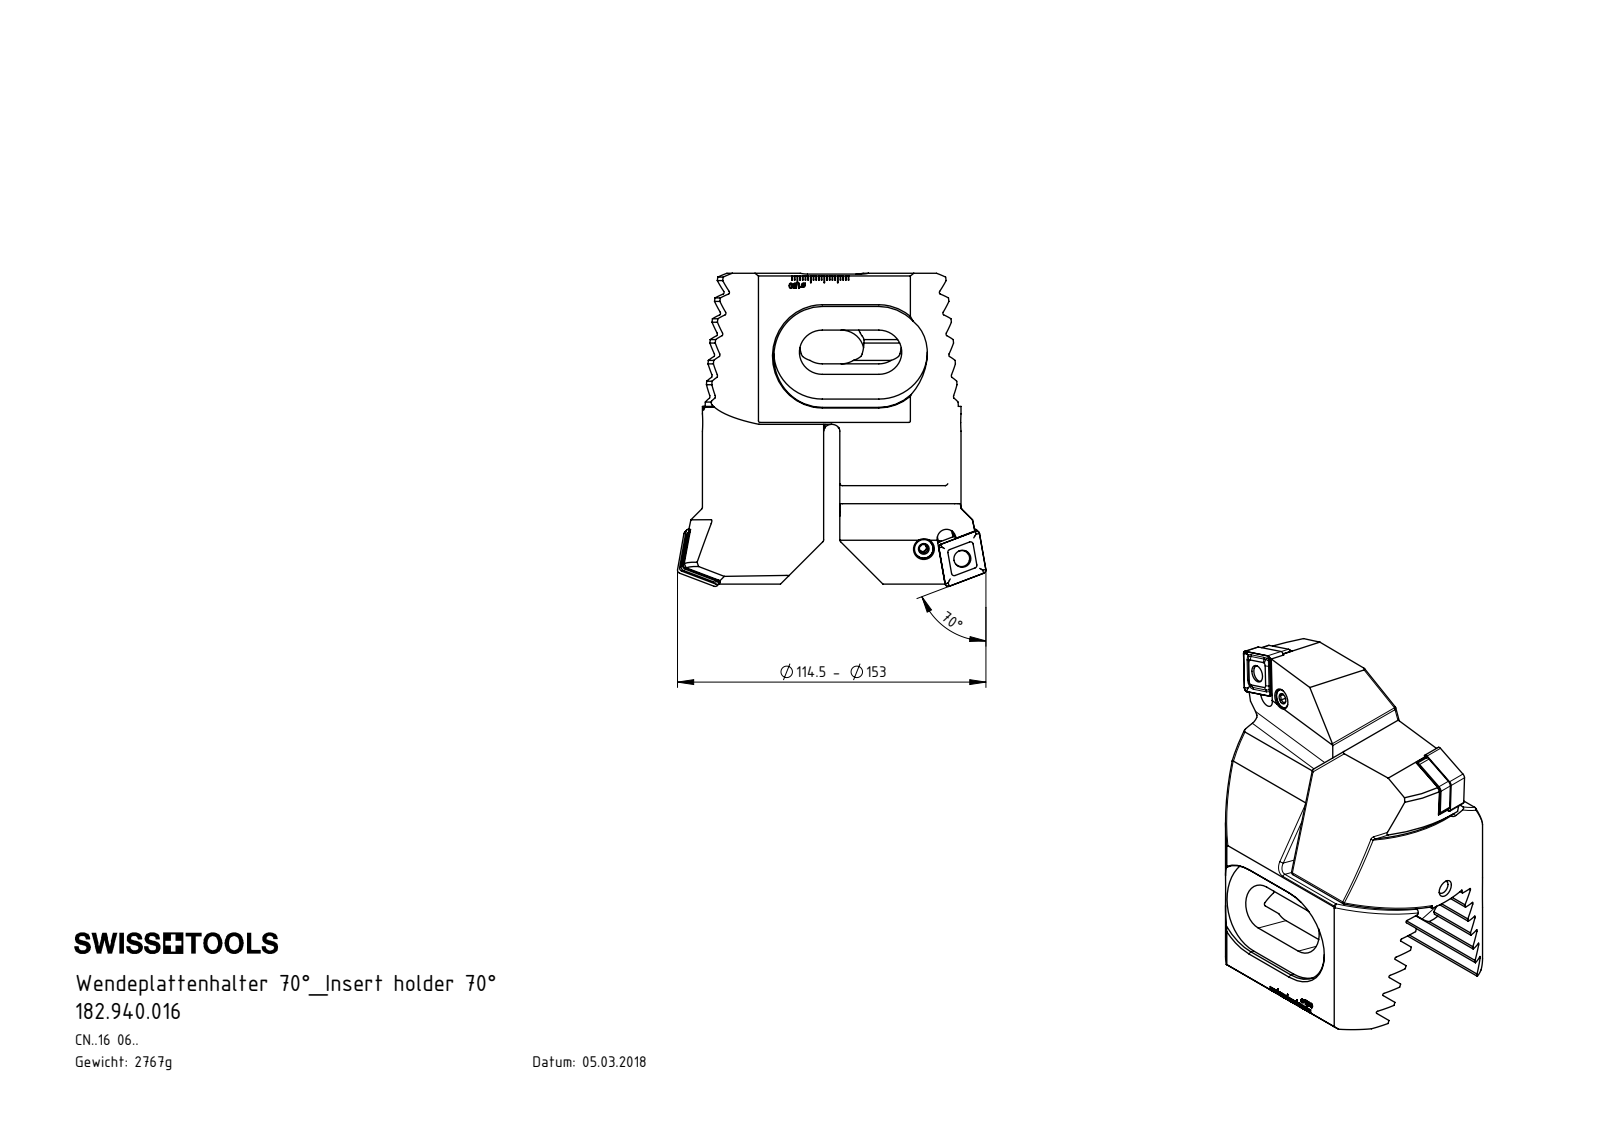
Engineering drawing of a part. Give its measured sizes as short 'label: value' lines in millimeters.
name: WCE-ER1.101.000; WCE-ER2.101.004_A; WCE; CNMG160612 (+5 more)
written by: SolidWorks 2017 (CONFIG_CONTROL_DESIGN)
unit: mm
bodies: 14 solids, 962 faces (536 planar, 168 cylindrical, 258 other)
size: 116.2 × 114.5 × 75.2
volume: 351 479 mm³; area: 70 327 mm²
holes: 2× ⌀2, 2× ⌀6.35, 2× ⌀7, 2× ⌀8.05, 2× ⌀8.4, 1× ⌀5
bosses: 3× ⌀6, 2× ⌀8, 2× ⌀7.9, 2× ⌀6.4, 2× ⌀3.55, 1× ⌀4
rounds: 16× R1, 12× R0.58, 8× R1.2, 8× R1.5, 6× R3, 6× R3.5, 4× R0.3, 4× R8.5
face distances: 6.93, 13.86, 20.79, 27.71, 13.19, 6, 20.78, 1.59, 13.85, 27.72
hole spacings: 14.78, 15, 25, 48.3
